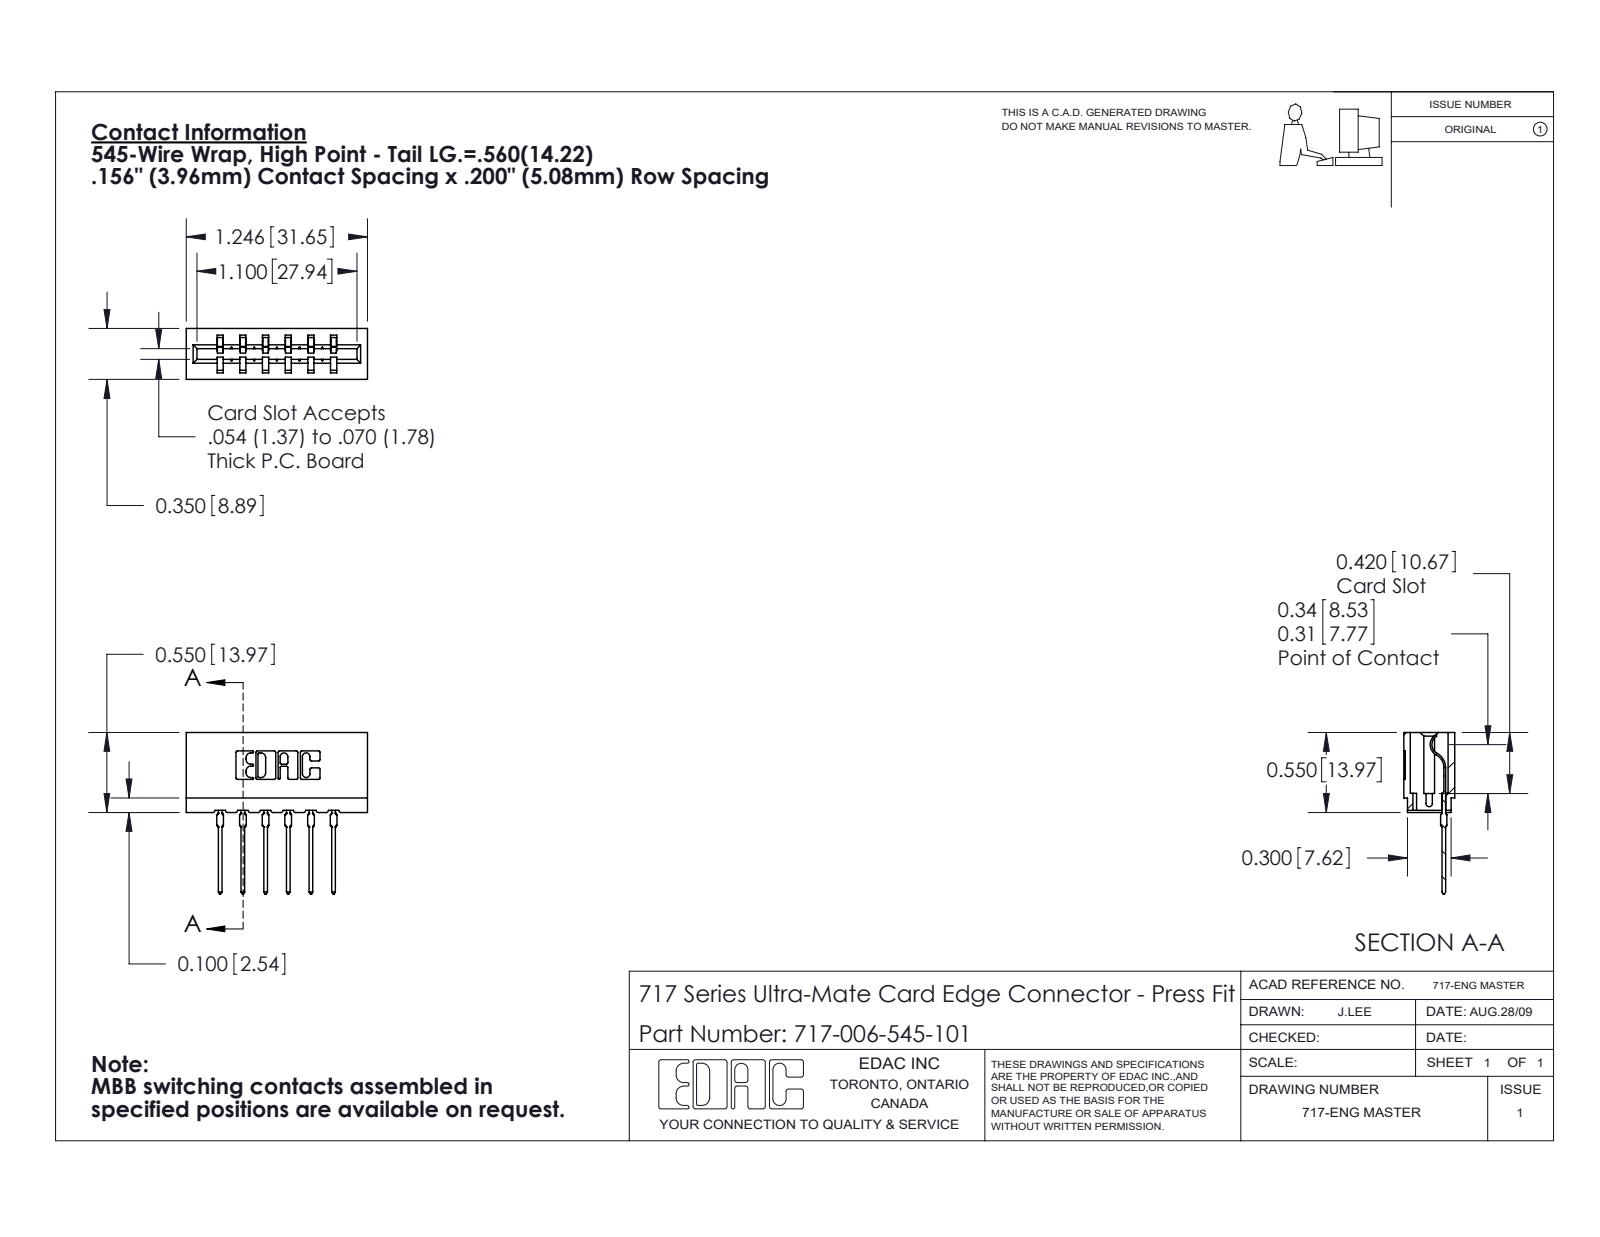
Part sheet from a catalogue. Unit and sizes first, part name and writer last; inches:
Units: inches
Overall size (bounding box): 1.246 × 1.109 × 0.35
Partial cylindrical surfaces — rounded edges, fillets, slot ends (radius × count): R0.01 ×22, R0.015 ×12, R0.021 ×12, R0.007 ×6, R0.031 ×6, R0.005 ×4, R0.011 ×4, R0.026 ×3
Main face-to-face distances: 0.212, 0.156, 0.138, 0.35, 0.198, 0.312, 0.624, 0.042, 0.312, 0.468
Volume: 0.174 in³ · Surface area: 5.75 in²
Bodies: 7 solids, 772 faces (462 planar, 154 cylindrical, 156 other)
Part name (STEP PRODUCT): 717 Part_Insulator Option - 06; 717-006-545-101; 745-292-001_545
STEP written by: SolidWorks 2020 (CONFIG_CONTROL_DESIGN)
